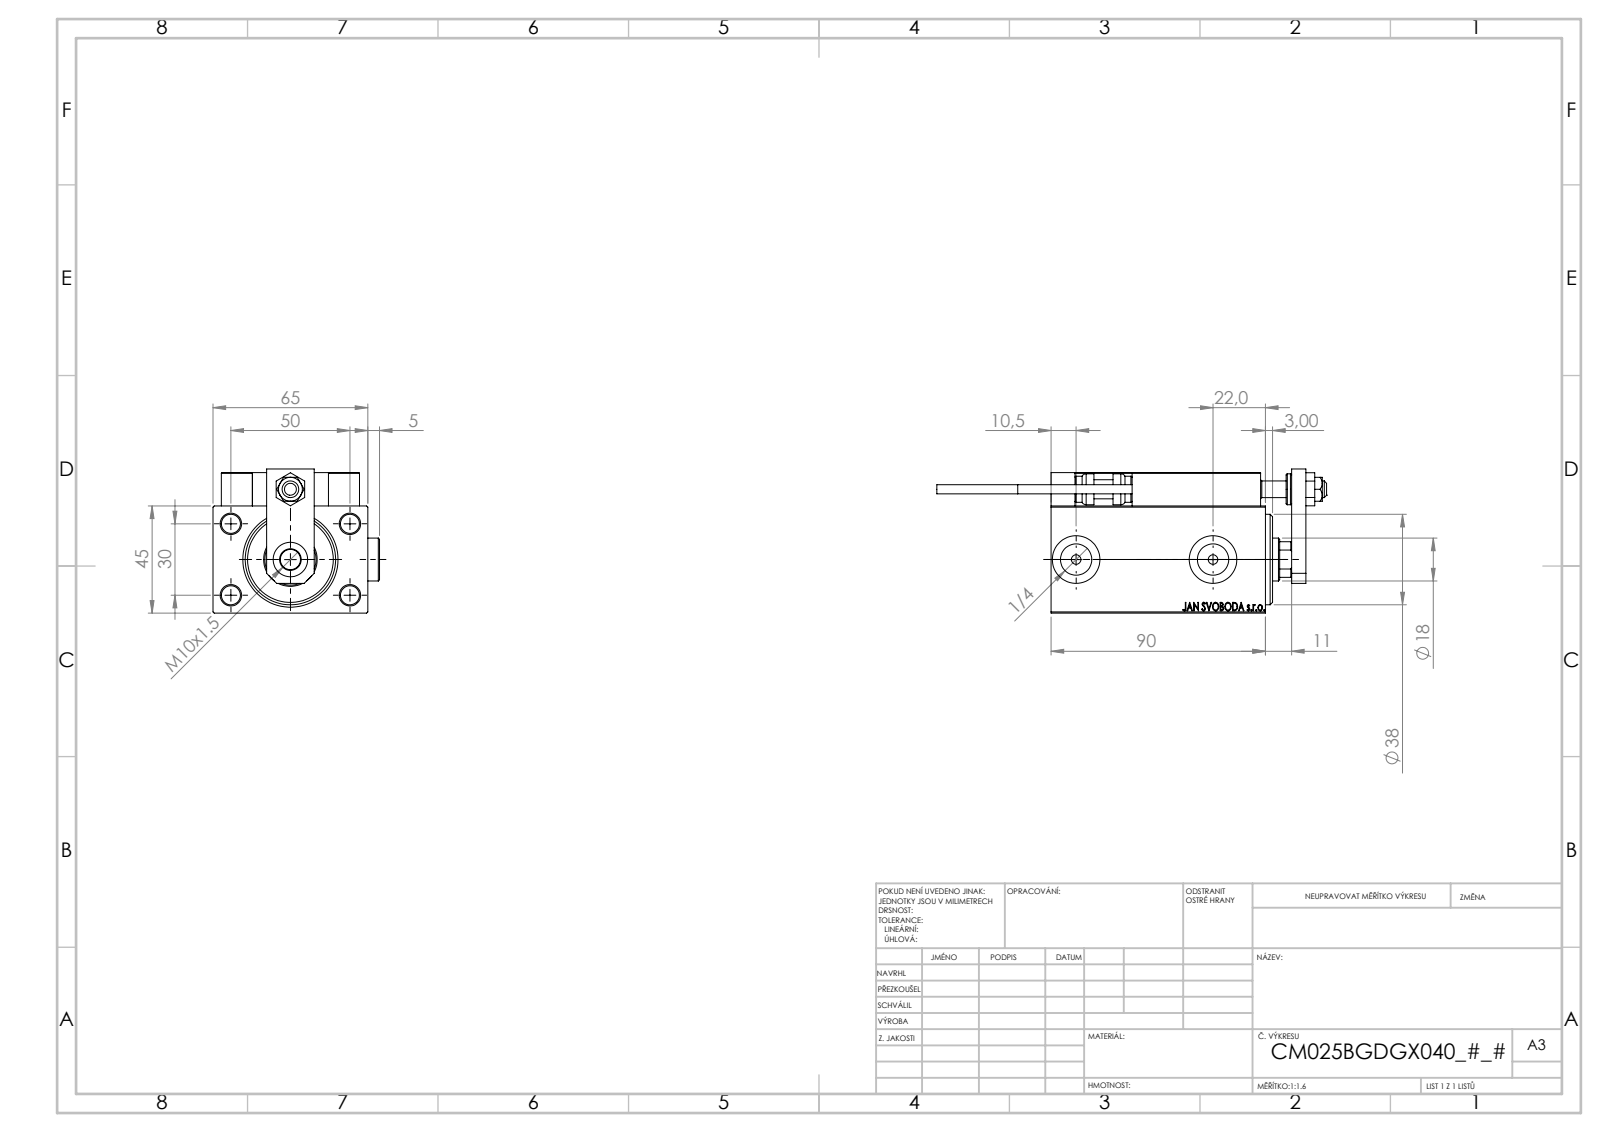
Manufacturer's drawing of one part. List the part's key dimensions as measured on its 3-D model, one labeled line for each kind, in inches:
Part name (STEP PRODUCT): V450CM_VC_B; NUT_D12; V450CM_B_VCP; V450CM_B_Body (+8 more)
STEP written by: SolidWorks 2019 (CONFIG_CONTROL_DESIGN)
Units: inches
Bodies: 26 solids, 1372 faces (595 planar, 200 cylindrical, 577 other)
Overall size (bounding box): 6.445 × 2.752 × 2.382
Volume: 17.84 in³ · Surface area: 115.9 in²
Round holes (diameter × count): ⌀0.315 ×9, ⌀0.157 ×6, ⌀0.126 ×4, ⌀0.197 ×2, ⌀0.518 ×2, ⌀0.787 ×2, ⌀0.276 ×1, ⌀0.335 ×1, ⌀0.571 ×1, ⌀0.709 ×1, ⌀0.846 ×1, ⌀0.886 ×1
Round bosses / shafts (diameter × count): ⌀0.709 ×2, ⌀0.197 ×2, ⌀0.15 ×2, ⌀0.512 ×1, ⌀0.433 ×1
Partial cylindrical surfaces — rounded edges, fillets, slot ends (radius × count): R0.012 ×30, R0.118 ×2, R0.335 ×1
Main face-to-face distances: 1.772, 2.559, 0.551, 0.236, 2.323, 0.197, 0.512, 0.138, 3.976, 0.748
Hole centre spacings: 1.148, 0.448, 0.787, 1.138, 1.165, 1.169, 1.181, 1.42
